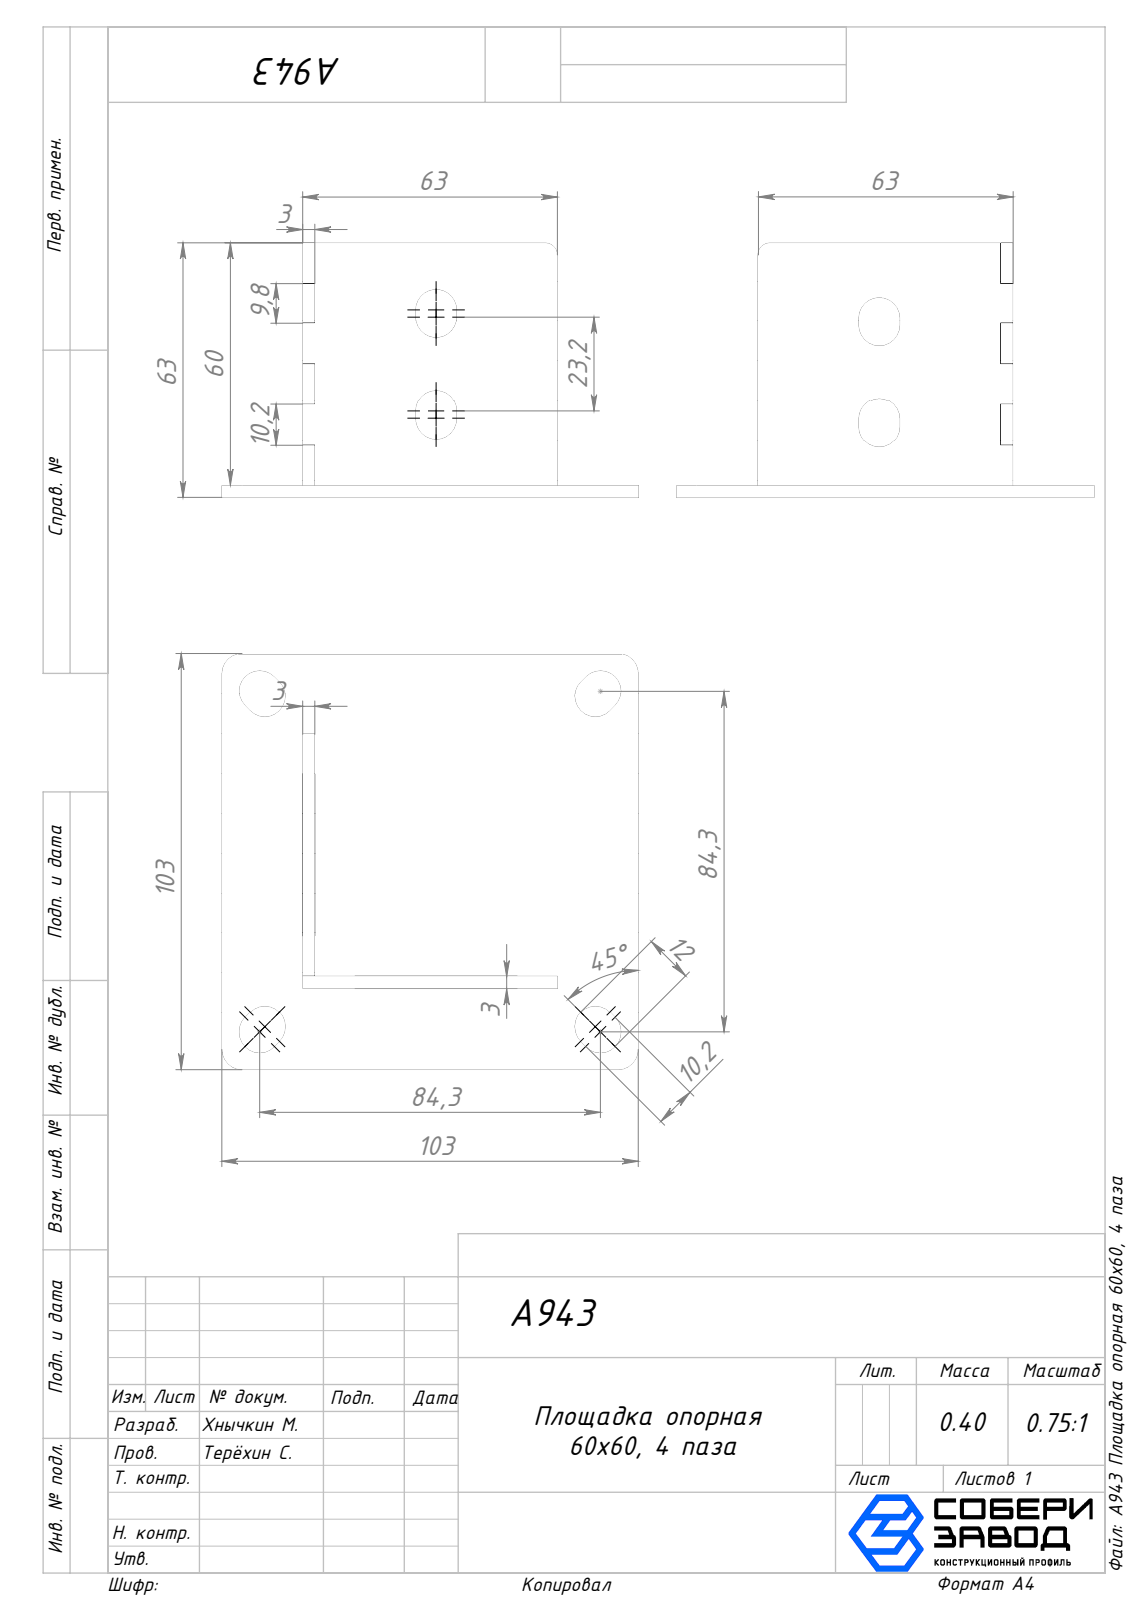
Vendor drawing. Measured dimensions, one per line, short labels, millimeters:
name: A943 60х60, 4 паза Боковина с пазом 1_00; A943 60х60, 4 паза Боковина с пазом 2_00; A943 Площадка опорная 60х60, 4 паза; A943 60х60 Основание 60х60, 4 паза_00
written by: SolidWorks 2025 (AUTOMOTIVE_DESIGN)
unit: mm
bodies: 3 solids, 98 faces (70 planar, 28 cylindrical, 0 other)
size: 103 × 103 × 63
volume: 51 424 mm³; area: 38 447 mm²
rounds: 16× R5.1, 4× R5, 2× R3
face distances: 3, 20, 83, 63, 60, 3.1, 23, 103, 80, 23.1
